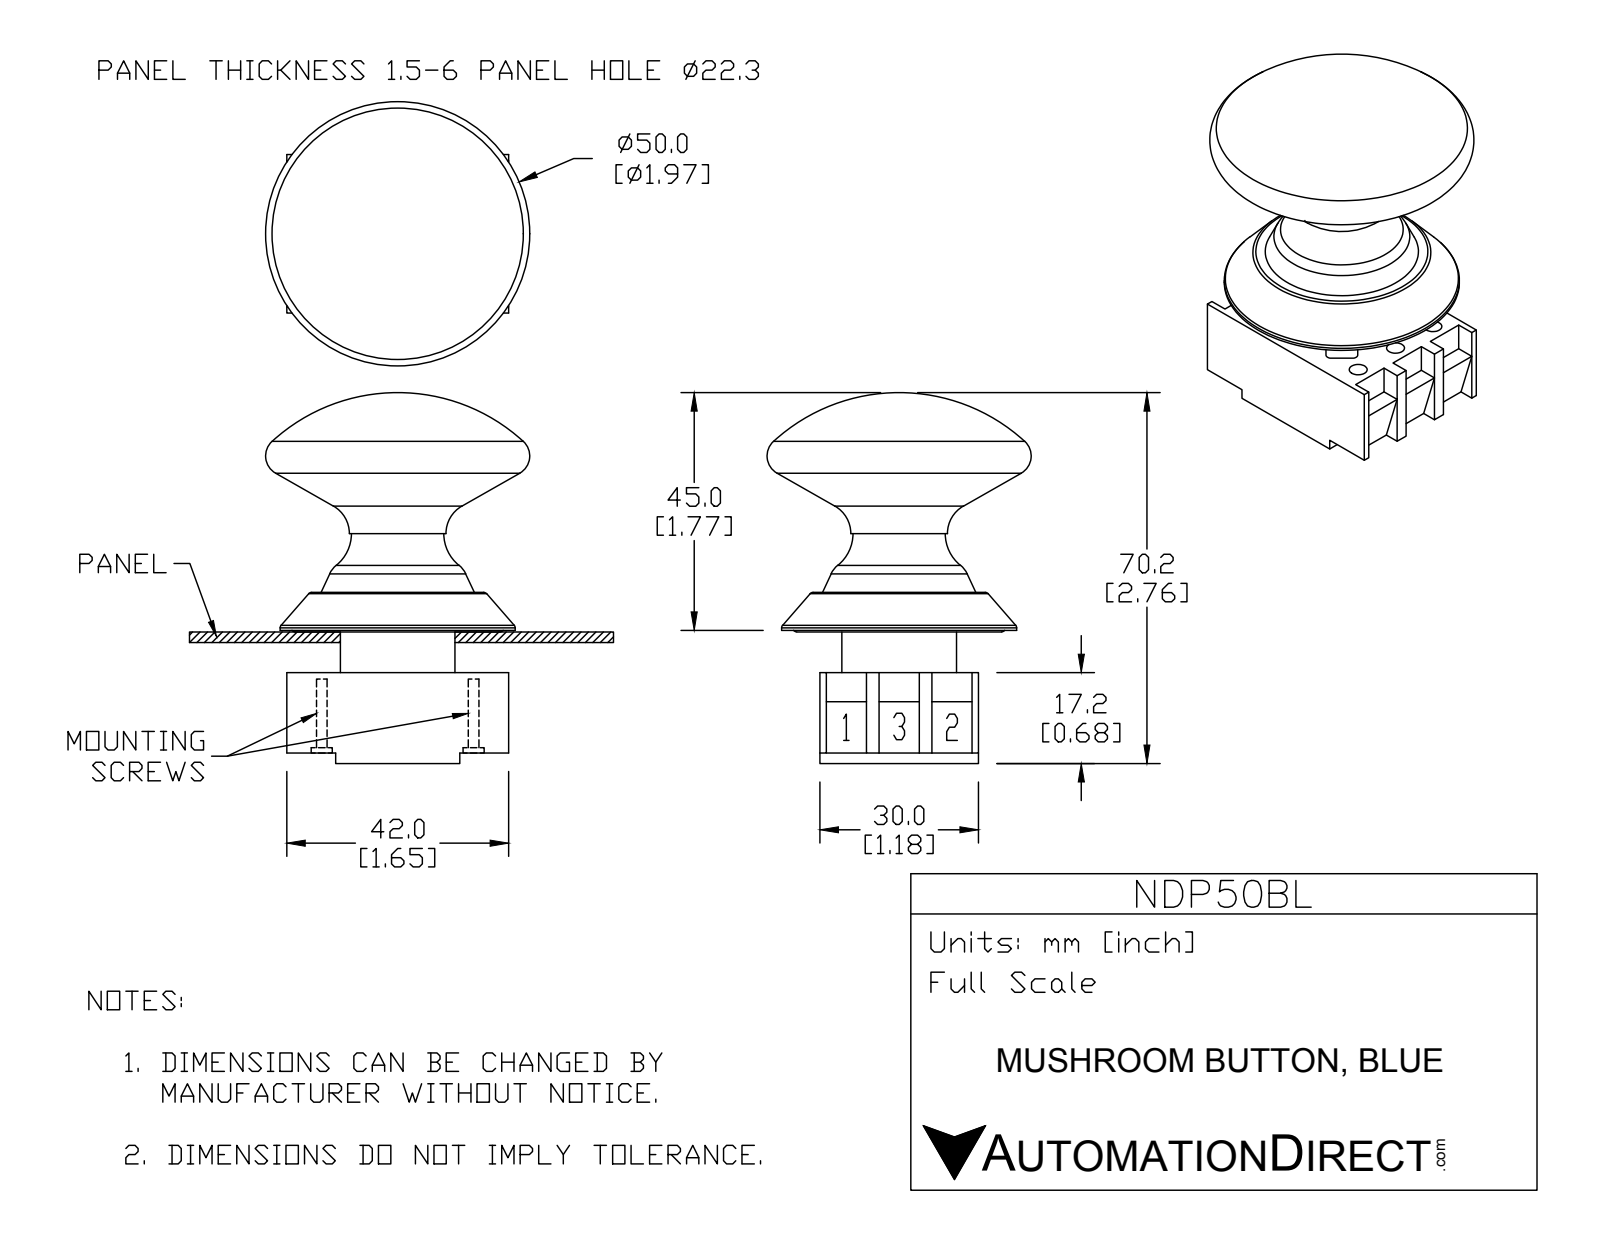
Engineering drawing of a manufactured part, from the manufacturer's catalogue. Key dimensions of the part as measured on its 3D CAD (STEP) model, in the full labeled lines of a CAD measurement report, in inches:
Part name (STEP PRODUCT): NDP50BL
STEP written by: SolidWorks 2015 (AUTOMOTIVE_DESIGN)
Units: inches
Bodies: 7 solids, 222 faces (126 planar, 63 cylindrical, 33 other)
Overall size (bounding box): 2.764 × 1.969 × 1.969
Volume: 3.399 in³ · Surface area: 33.49 in²
Round holes (diameter × count): ⌀0.134 ×6, ⌀0.197 ×6, ⌀0.492 ×1
Round bosses / shafts (diameter × count): ⌀0.181 ×2, ⌀0.157 ×2, ⌀1.752 ×1, ⌀0.854 ×1
Partial cylindrical surfaces — rounded edges, fillets, slot ends (radius × count): R0.039 ×8, R0.343 ×5, R0.433 ×1
Main face-to-face distances: 0.283, 0.598, 1.181, 0.315, 0.295, 0.303, 0.902, 0.394, 0.913, 1.197
Hole centre spacings: 0.394, 0.69, 1.199, 1.132, 0.566, 0.787, 1.379
